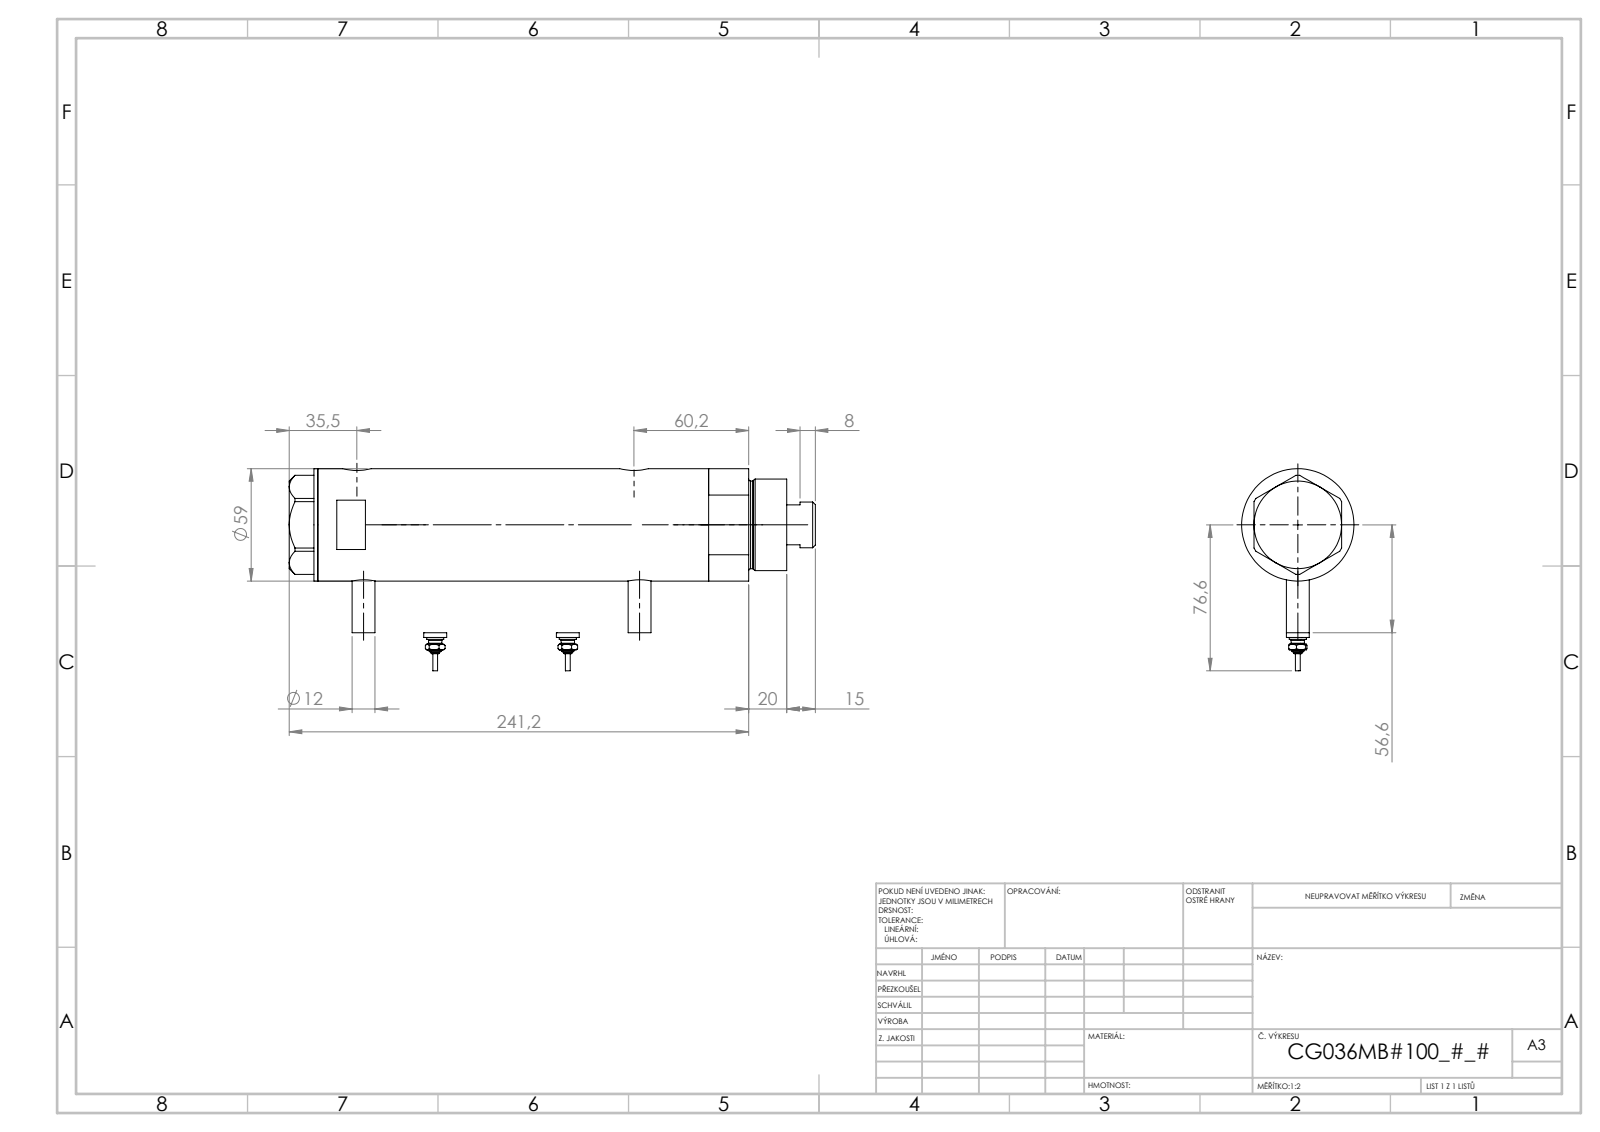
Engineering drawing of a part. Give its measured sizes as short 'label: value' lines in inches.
name: V270CG_BACK; V270CG_SWITCH; V270CG_FRONT; V270CG_VC (+1 more)
written by: SolidWorks 2019 (CONFIG_CONTROL_DESIGN)
unit: in
bodies: 6 solids, 232 faces (81 planar, 77 cylindrical, 74 other)
size: 10.371 × 3.594 × 2.323
volume: 36.29 in³; area: 188.4 in²
holes: 2× ⌀0.197, 2× ⌀0.383, 2× ⌀0.492, 2× ⌀0.591, 1× ⌀0.335, 1× ⌀0.984, 1× ⌀1.043, 1× ⌀1.417, 1× ⌀1.575, 1× ⌀2.047
bosses: 4× ⌀0.472, 2× ⌀0.354, 2× ⌀0.276, 2× ⌀0.171, 2× ⌀0.094, 1× ⌀2.323, 1× ⌀1.89, 1× ⌀1.811
face distances: 6.194, 0.925, 5.269, 0.591, 1.516, 6.785, 9.78, 9.19, 8.265, 2.995
hole spacings: 0.114, 0.138, 5.203, 5.317, 5.341, 5.455, 0.114, 0.115
